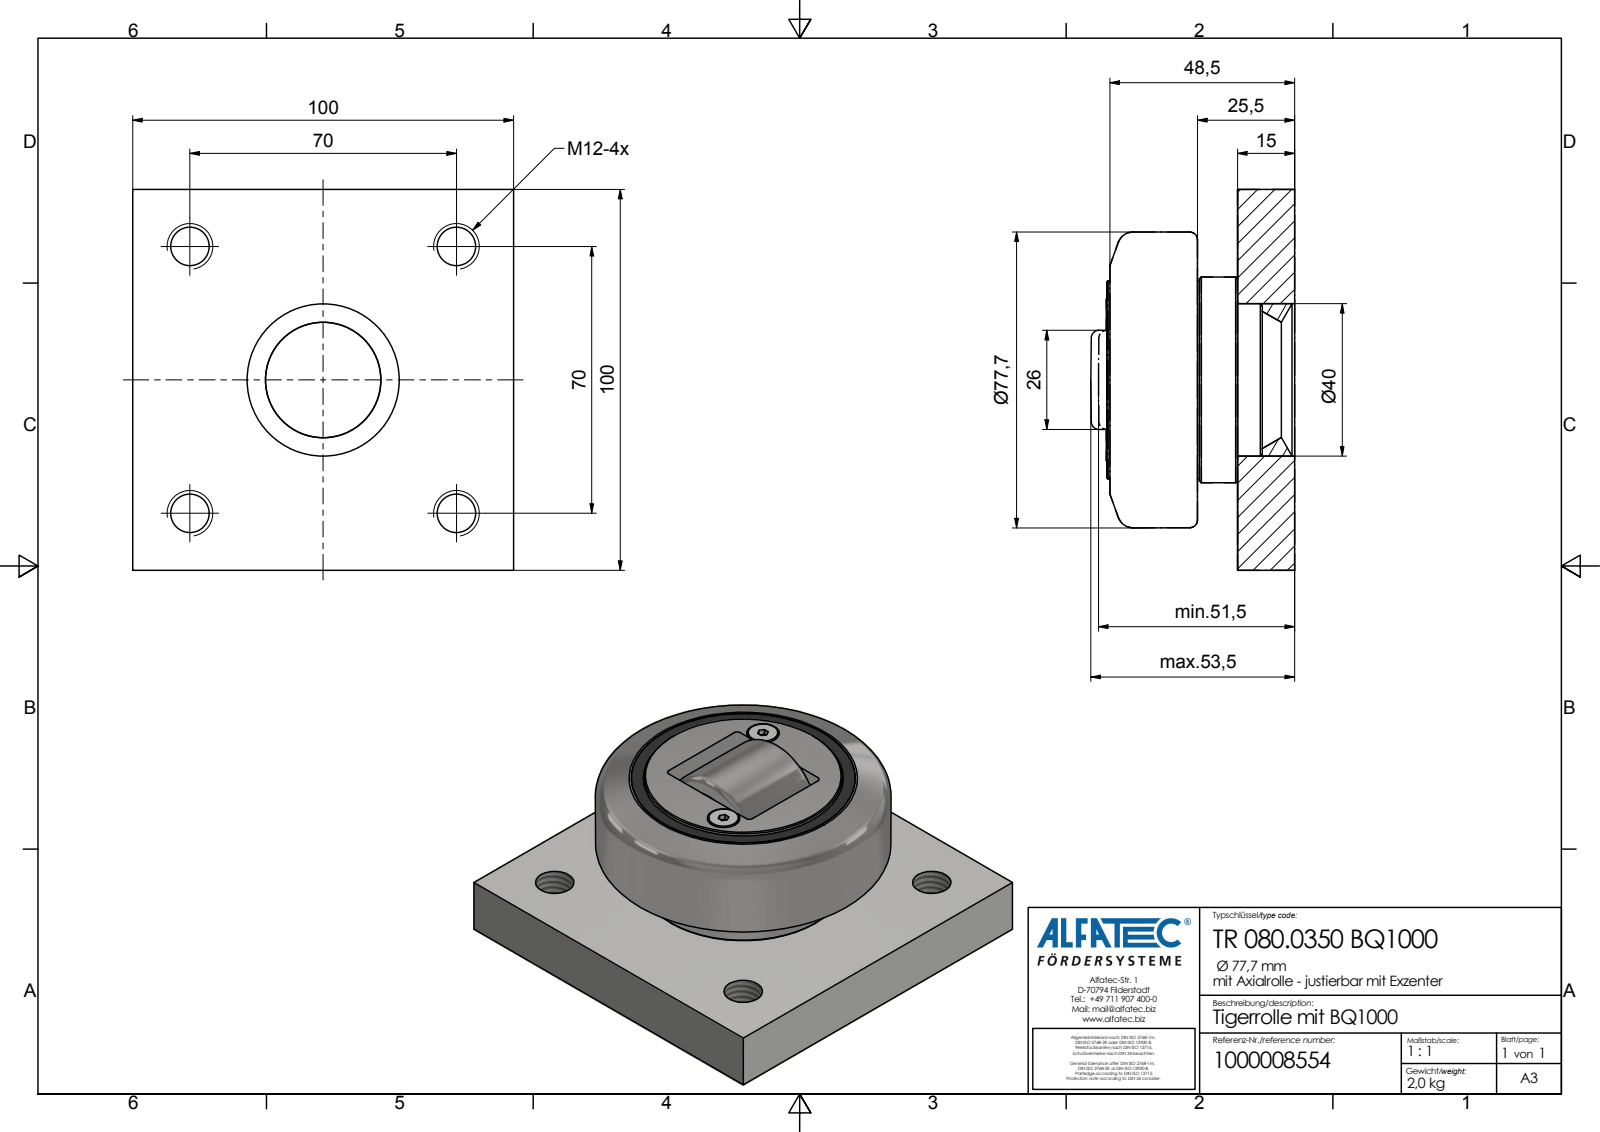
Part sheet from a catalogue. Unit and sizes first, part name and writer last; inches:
Units: inches
Overall size (bounding box): 3.937 × 3.937 × 2.106
Round holes (diameter × count): ⌀0.398 ×4, ⌀1.575 ×1
Round bosses / shafts (diameter × count): ⌀0.307 ×2, ⌀2.126 ×1, ⌀2.047 ×1
Partial cylindrical surfaces — rounded edges, fillets, slot ends (radius × count): R0.039 ×4, R0.443 ×1
Main face-to-face distances: 0.591, 3.937, 1.004, 0.413, 1.941, 1.35, 0.937, 1.909, 1.319, 0.906
Hole centre spacings: 1.949, 2.756, 3.897
Volume: 16.7 in³ · Surface area: 61.28 in²
Bodies: 1 solid, 65 faces (36 planar, 16 cylindrical, 13 other)
Part name (STEP PRODUCT): TR 080.0350 BQ1000_Kontur
STEP written by: Autodesk Inventor 2020 (AP242_MANAGED_MODEL_BASED_3D_ENGINEERING_MIM_LF)
